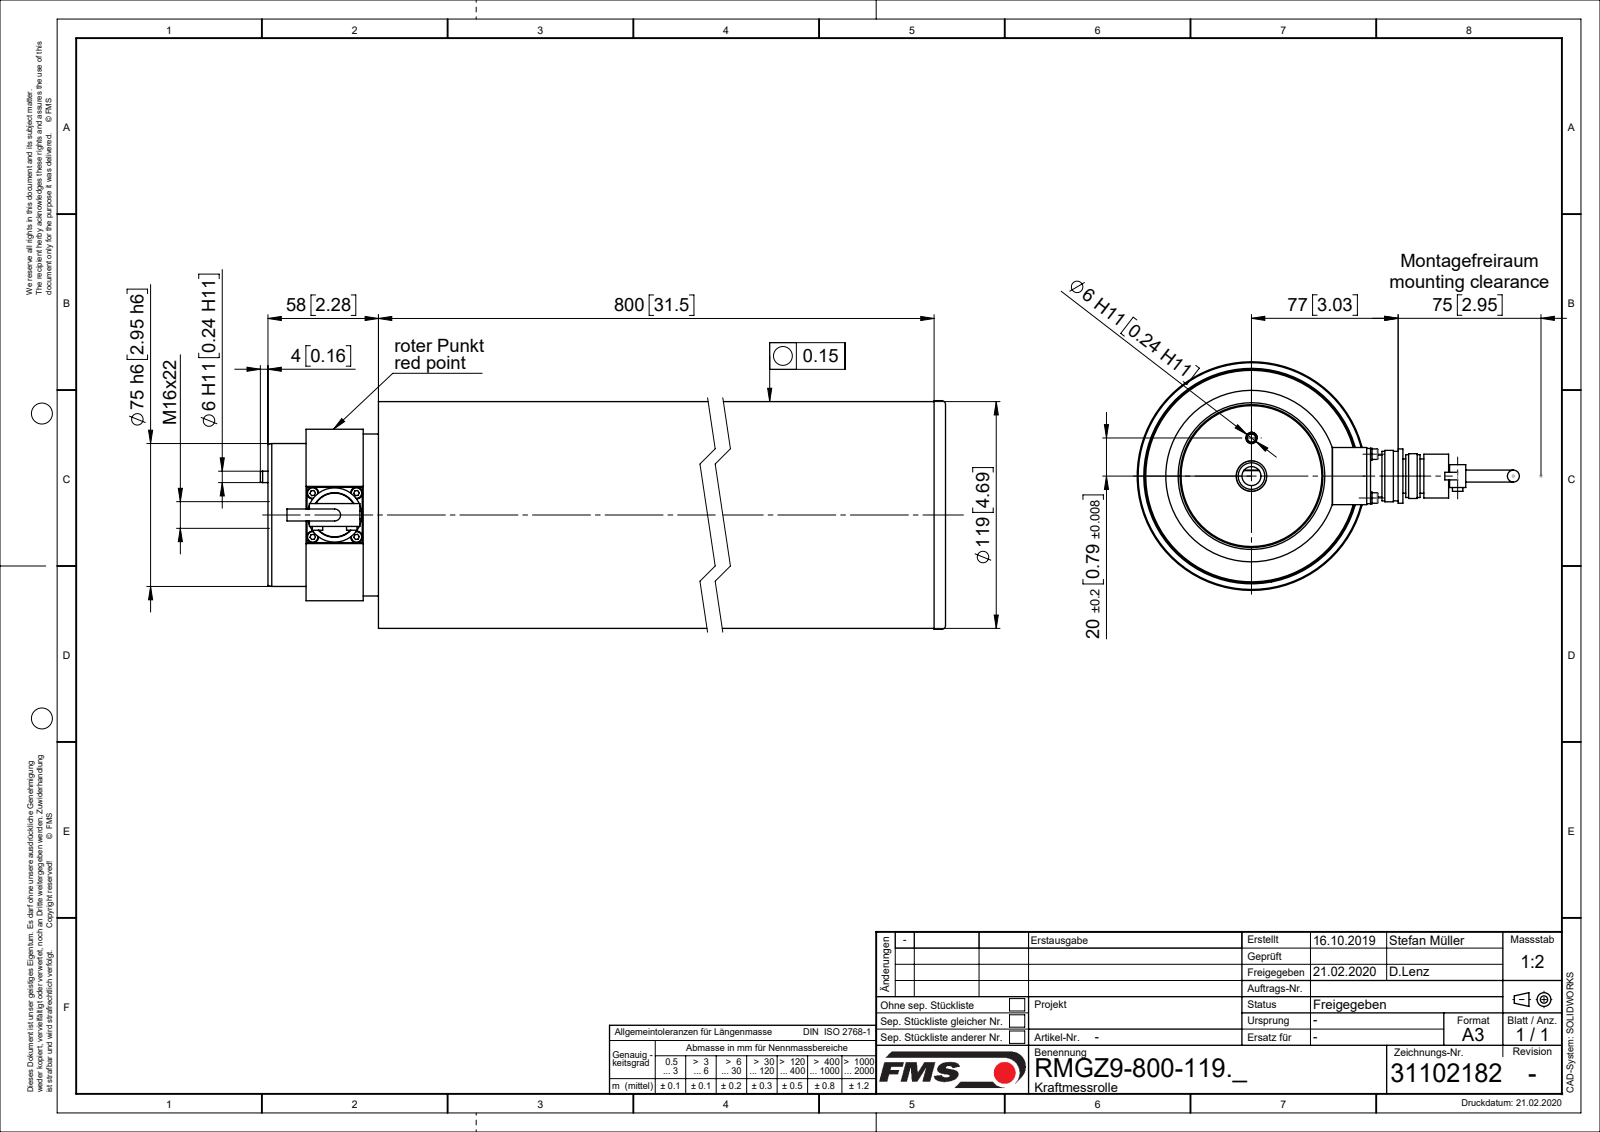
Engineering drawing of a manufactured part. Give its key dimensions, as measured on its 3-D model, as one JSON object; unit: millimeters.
{"part_name": "47726-04_stp_01; Lamellenstopfen_D_120; Zyl-Schr DIN912_M3x25; 130507.6_01 (+8 more)", "step_written_by": "SolidWorks 2018 (CONFIG_CONTROL_DESIGN)", "units": "millimeters", "bodies": {"solids": 31, "faces": 570, "planar": 162, "cylindrical": 234, "other": 174}, "overall_size": [868, 200.65, 120], "volume_mm3": 3358000, "surface_area_mm2": 887810, "round_holes": [[2.5, 4], [3.1, 4], [3.4, 4], [3.3, 1], [5, 1], [6, 1], [10, 1], [12, 1], [14, 1], [22, 1], [23, 1], [26, 1]], "round_bosses_or_shafts": [[5.5, 6], [6.2, 4], [3, 4], [2.5, 4], [120, 1], [119, 1], [111, 1], [106, 1]], "partial_cylinders_radius": [[11, 4], [4.25, 2], [17.5, 1]], "face_to_face_distances": [32, 241, 2, 50, 227, 466, 253, 605, 273, 498], "hole_center_spacings": [16.26, 23, 32.53, 20]}
